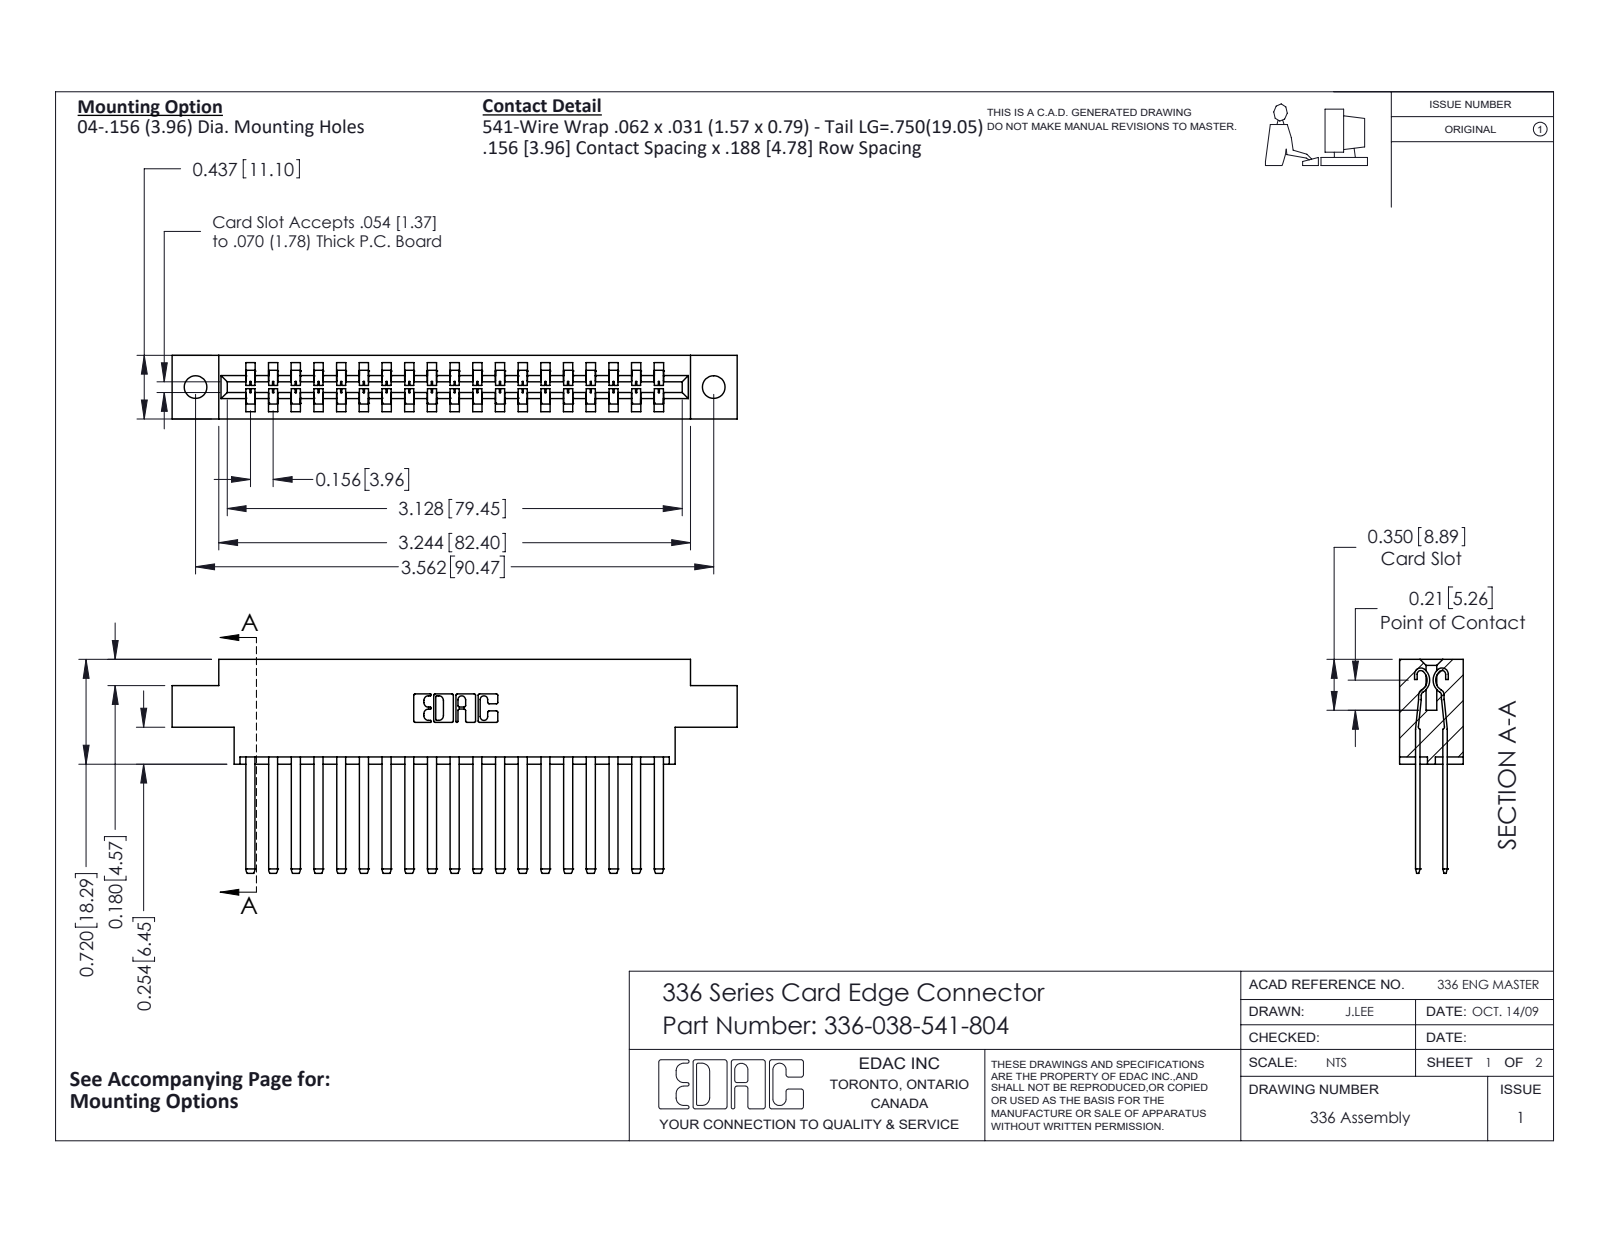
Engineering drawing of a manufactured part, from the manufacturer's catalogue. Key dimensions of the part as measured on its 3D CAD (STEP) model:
Part name (STEP PRODUCT): 336-038-541-804; 336 Part_Offset - .156 Dia - TH; 336-290-001_336-290-541
STEP written by: SolidWorks 2020 (CONFIG_CONTROL_DESIGN)
Units: inches
Bodies: 39 solids, 1714 faces (1062 planar, 652 cylindrical, 0 other)
Overall size (bounding box): 3.885 × 1.47 × 0.437
Volume: 0.878 in³ · Surface area: 27.62 in²
Round holes (diameter × count): ⌀0.156 ×2
Partial cylindrical surfaces — rounded edges, fillets, slot ends (radius × count): R0.004 ×76, R0.056 ×38, R0.01 ×22, R0.007 ×6, R0.031 ×6, R0.022 ×4, R0.04 ×4, R0.026 ×3
Main face-to-face distances: 0.188, 0.328, 0.14, 0.297, 0.109, 0.031, 0.437, 0.033, 0.181, 0.256
Hole centre spacings: 3.562
